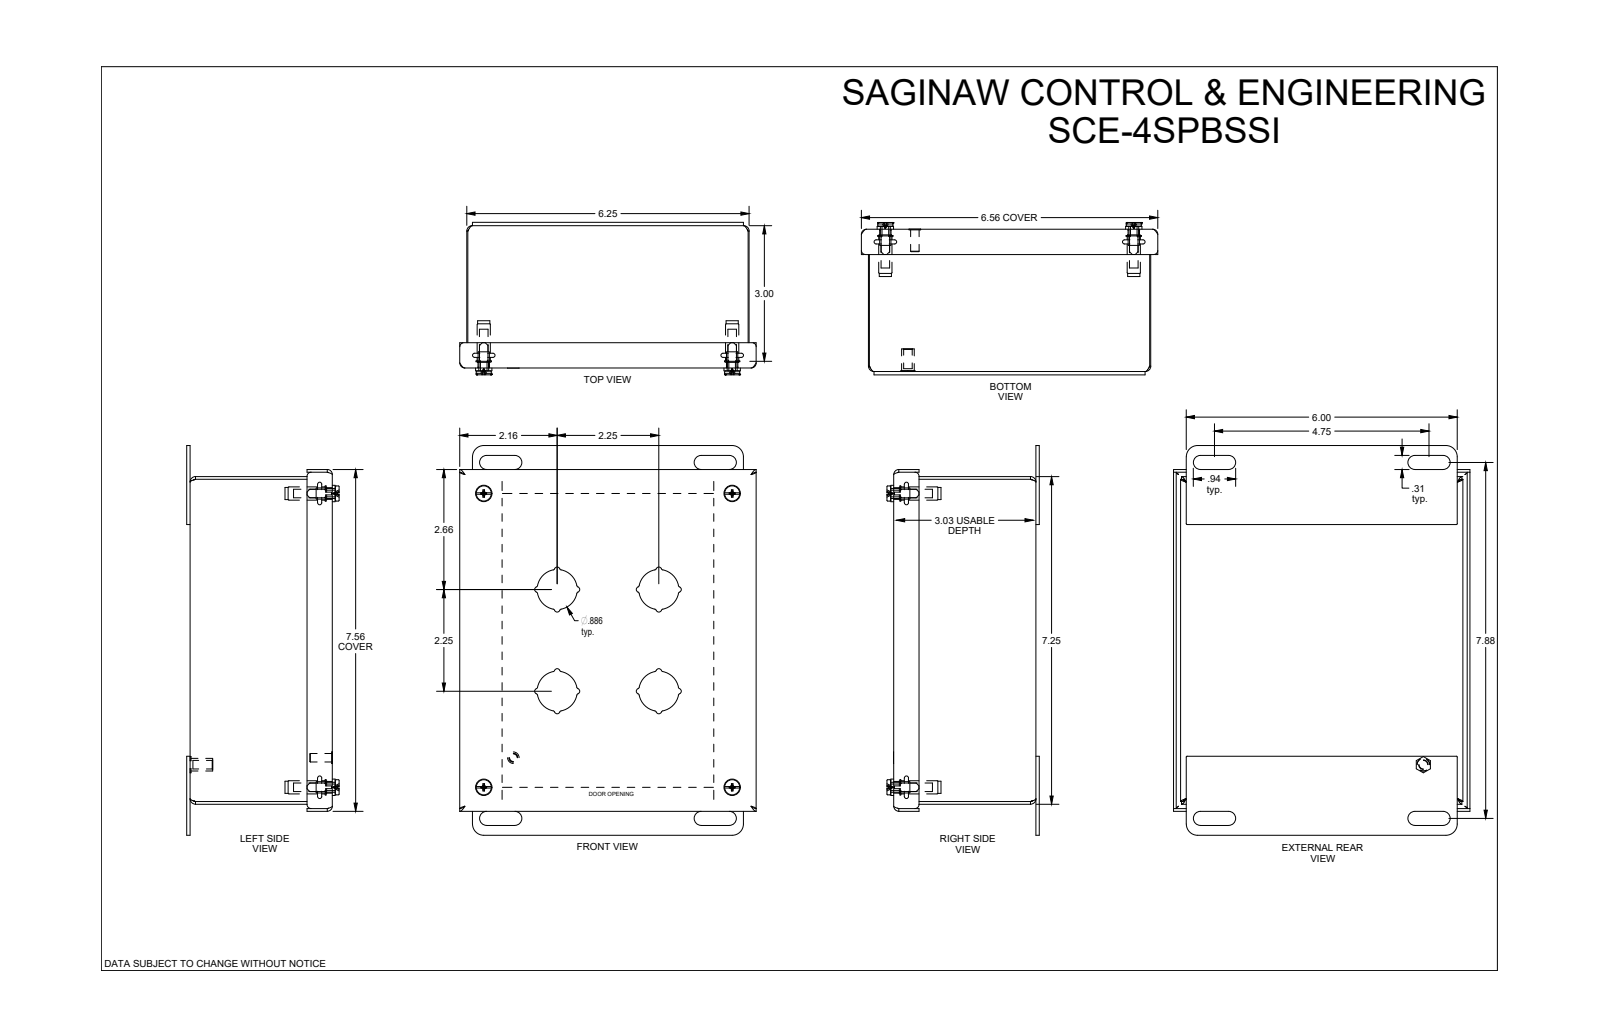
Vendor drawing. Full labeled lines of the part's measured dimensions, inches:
Part name (STEP PRODUCT): SCE-4SPBSSI
STEP written by: SolidWorks 2021 (AUTOMOTIVE_DESIGN)
Units: inches
Bodies: 3 solids, 484 faces (149 planar, 243 cylindrical, 92 other)
Overall size (bounding box): 8.625 × 6.563 × 3.286
Volume: 13.71 in³ · Surface area: 427.8 in²
Round holes (diameter × count): ⌀0.19 ×5, ⌀0.22 ×4, ⌀0.266 ×4, ⌀0.27 ×4, ⌀0.317 ×4
Round bosses / shafts (diameter × count): ⌀0.5 ×4, ⌀0.415 ×4, ⌀0.362 ×4, ⌀0.296 ×4, ⌀0.26 ×4, ⌀0.28 ×1, ⌀0.256 ×1, ⌀0.188 ×1
Partial cylindrical surfaces — rounded edges, fillets, slot ends (radius × count): R0.04 ×32, R0.06 ×20, R0.062 ×16, R0.015 ×8, R0.115 ×8, R0.156 ×8, R0.245 ×8, R0.02 ×4
Main face-to-face distances: 0.06, 3.088, 3.028, 6.19, 3.148, 7.19, 0.156, 6.25, 6.13, 0.075
Hole centre spacings: 8.515, 5.5, 5.5, 6.5, 6.5, 8.514, 0.7, 0.707
